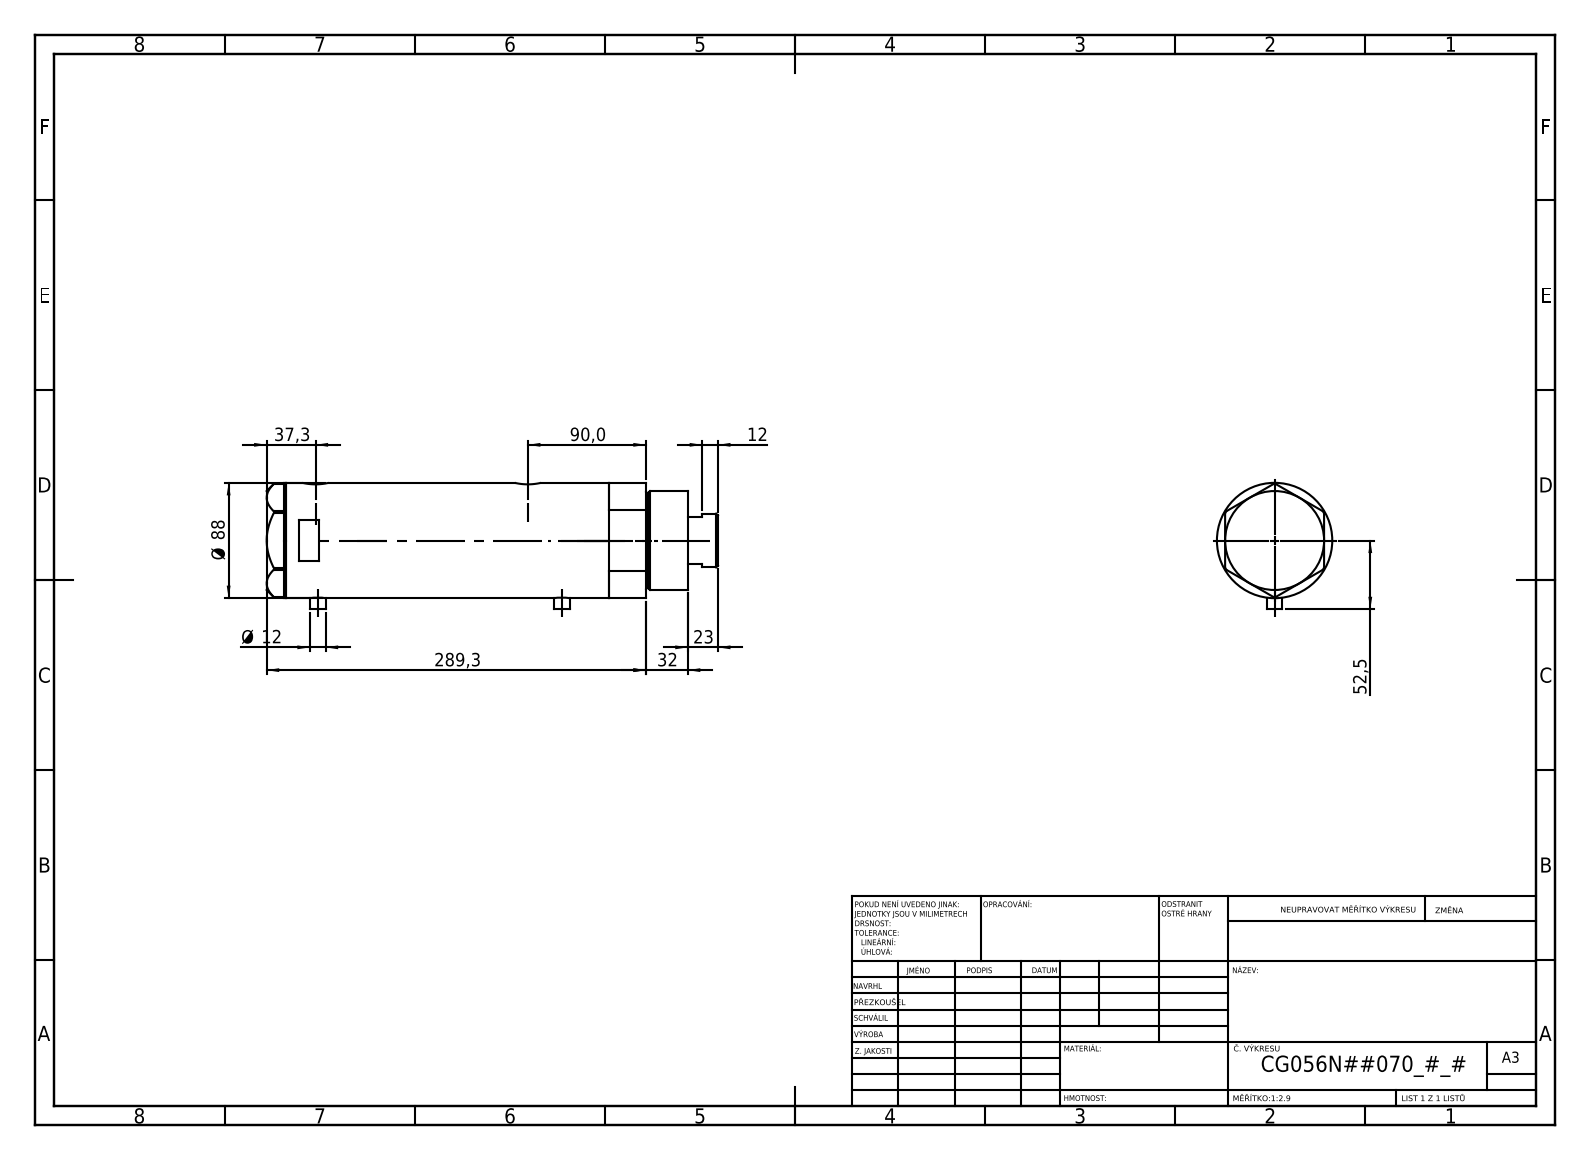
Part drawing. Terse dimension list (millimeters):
name: V270CG_BACK; V270CG_FRONT; V270CG_MIDDLE; V270CG_VC
written by: SolidWorks 2019 (CONFIG_CONTROL_DESIGN)
unit: mm
bodies: 4 solids, 121 faces (52 planar, 49 cylindrical, 20 other)
size: 344.3 × 96.5 × 88
volume: 1 817 000 mm³; area: 251 970 mm²
holes: 2× ⌀12.5, 2× ⌀13.16, 2× ⌀20, 1× ⌀14.5, 1× ⌀42, 1× ⌀43.5, 1× ⌀56, 1× ⌀60, 1× ⌀80
bosses: 2× ⌀12, 1× ⌀88, 1× ⌀75, 1× ⌀73, 1× ⌀41
face distances: 184.4, 26, 158.4, 15, 41, 199.4, 306.3, 321.3, 280.3, 121.9
hole spacings: 1.7, 25.8, 160.3, 162, 186.1, 187.8
